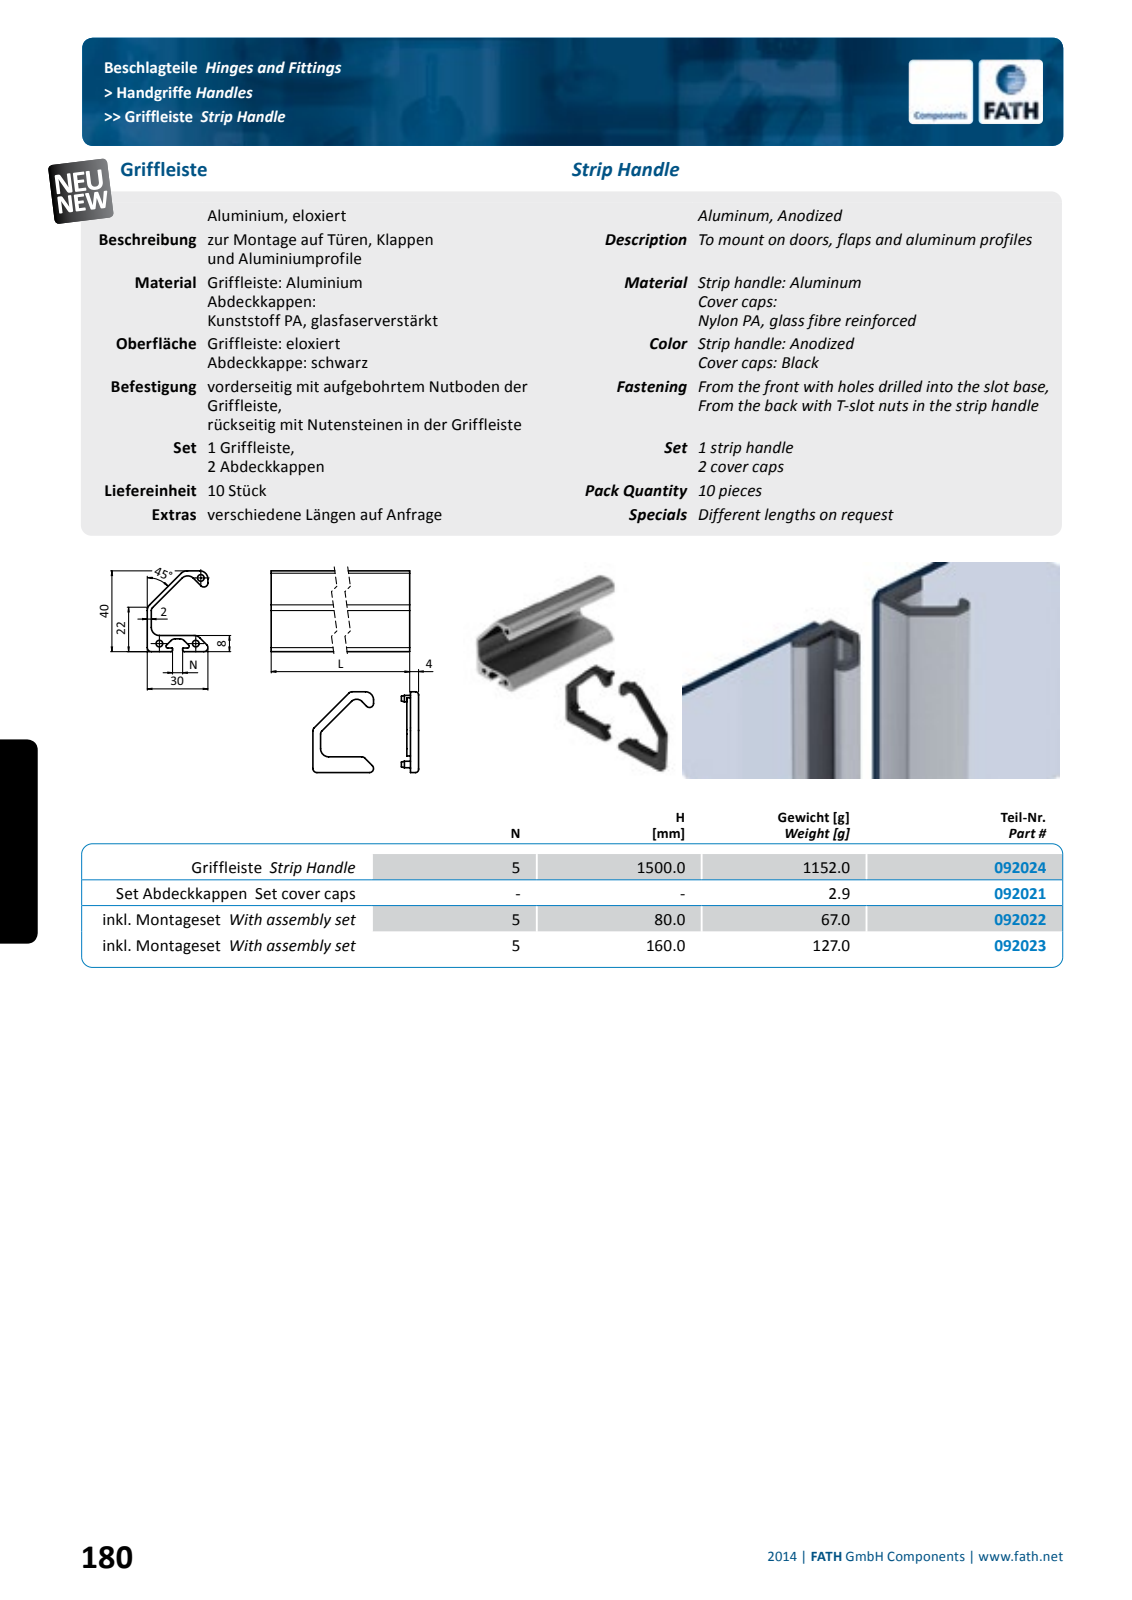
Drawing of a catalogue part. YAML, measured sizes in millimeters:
part_name: "fath_092023_1; fath_092023_2; fath_092023_3"
step_written_by: "Spatial InterOp 3D (automotive_design)"
units: millimeters
bodies: {solids: 3, faces: 261, planar: 108, cylindrical: 119, other: 34}
overall_size: [160, 127.6, 40]
volume: 47574
surface_area: 41309
round_holes:
  - {diameter: 1.9, count: 6}
  - {diameter: 3.3, count: 3}
round_bosses_or_shafts:
  - {diameter: 3.2, count: 6}
partial_cylinders:
  - {radius: 2, count: 18}
  - {radius: 1.5, count: 17}
  - {radius: 1, count: 12}
  - {radius: 4, count: 10}
  - {radius: 3, count: 6}
  - {radius: 0.3, count: 2}
  - {radius: 0.8, count: 2}
  - {radius: 0.83, count: 2}
face_to_face_distances: [2, 8, 1, 40, 32, 1.8, 18.62, 6.2, 38.2, 6.43]
hole_center_spacings: [18.2, 32.68, 36.81, 37.6, 38.51, 48.05, 59.9, 14.8]
